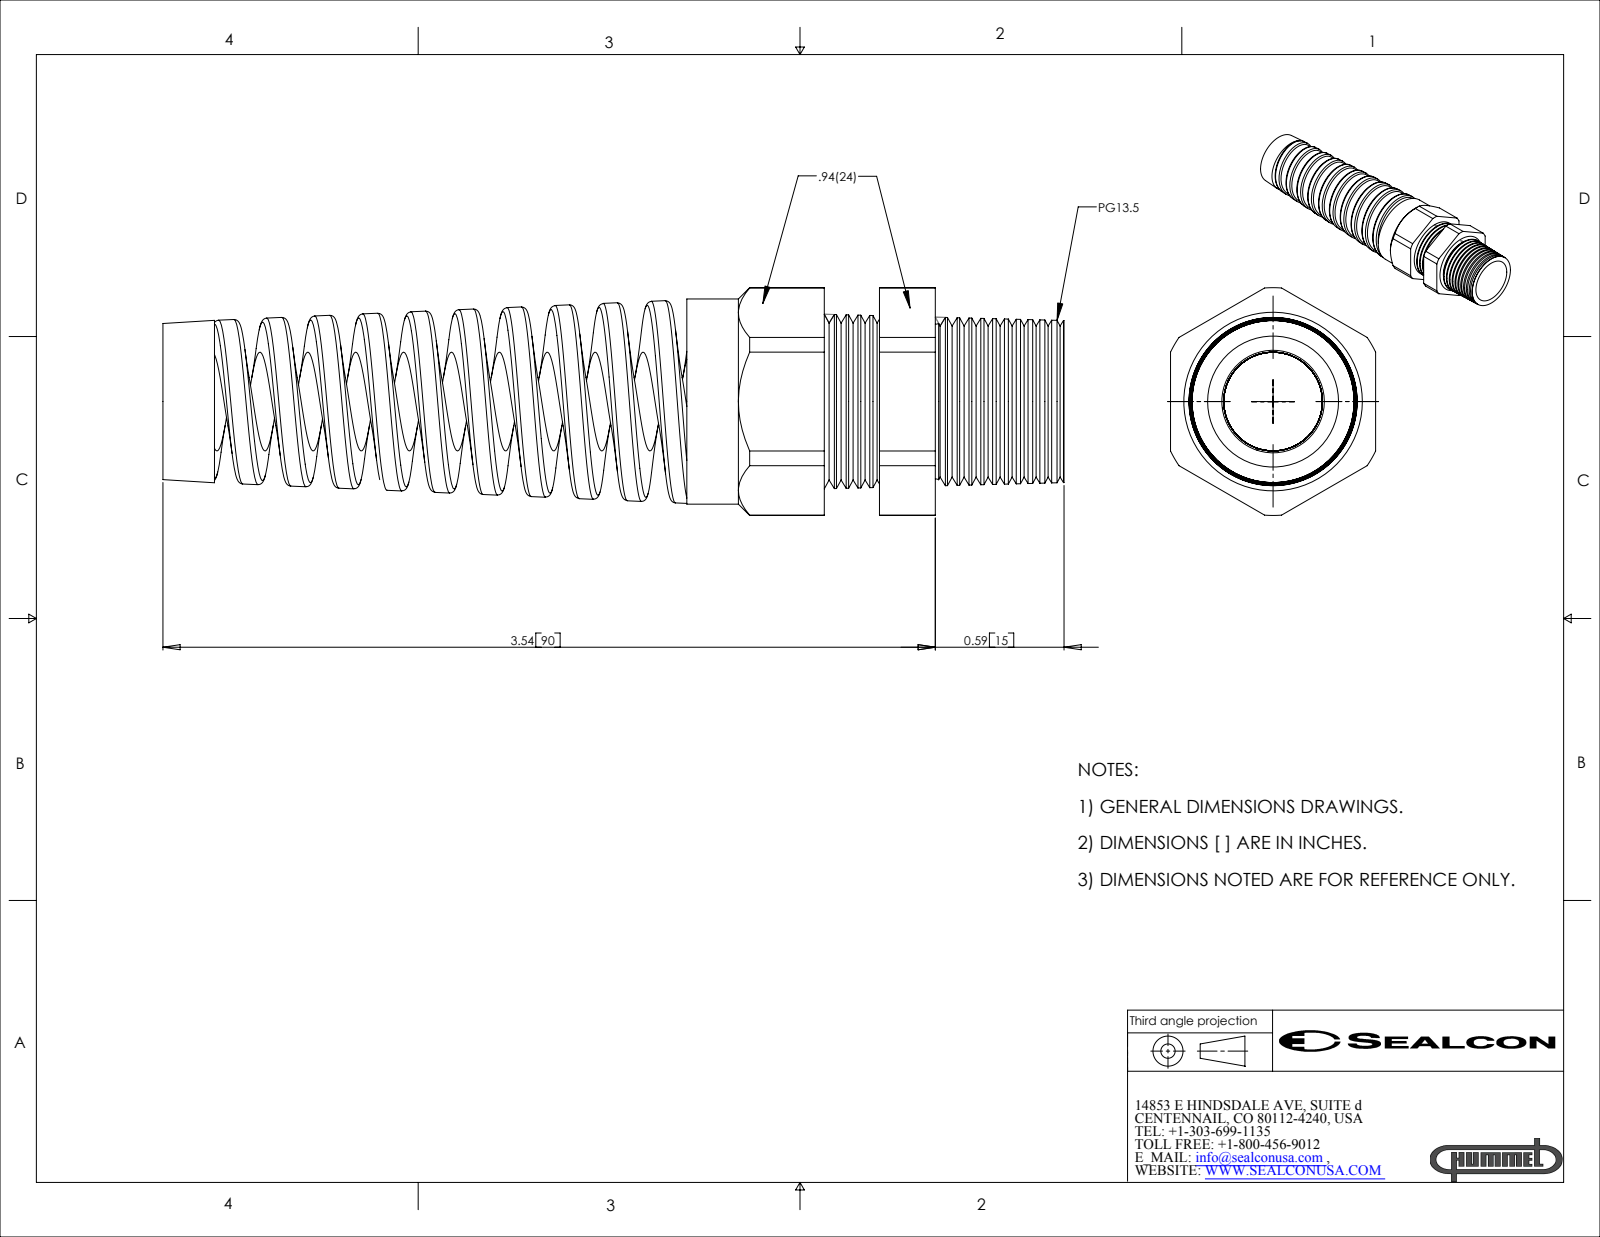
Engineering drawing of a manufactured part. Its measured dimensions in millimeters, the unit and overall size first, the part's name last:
Units: millimetres
Overall size (bounding box): 104.9 × 26.5 × 23.9
Round holes (diameter × count): ⌀11.5 ×1, ⌀11.9 ×1, ⌀12.2 ×1
Round bosses / shafts (diameter × count): ⌀23.9 ×1, ⌀15.2 ×1
Partial cylindrical surfaces — rounded edges, fillets, slot ends (radius × count): R13.3 ×1
Main face-to-face distances: 23.9, 61, 6.4, 6, 16, 22.4, 28.9, 12.9, 6.5, 77
Volume: 19 520 mm³ · Surface area: 15 710 mm²
Bodies: 2 solids, 209 faces (24 planar, 46 cylindrical, 139 other)
Part name (STEP PRODUCT): CF13CA-BK
STEP written by: SolidWorks 2007 (CONFIG_CONTROL_DESIGN)
